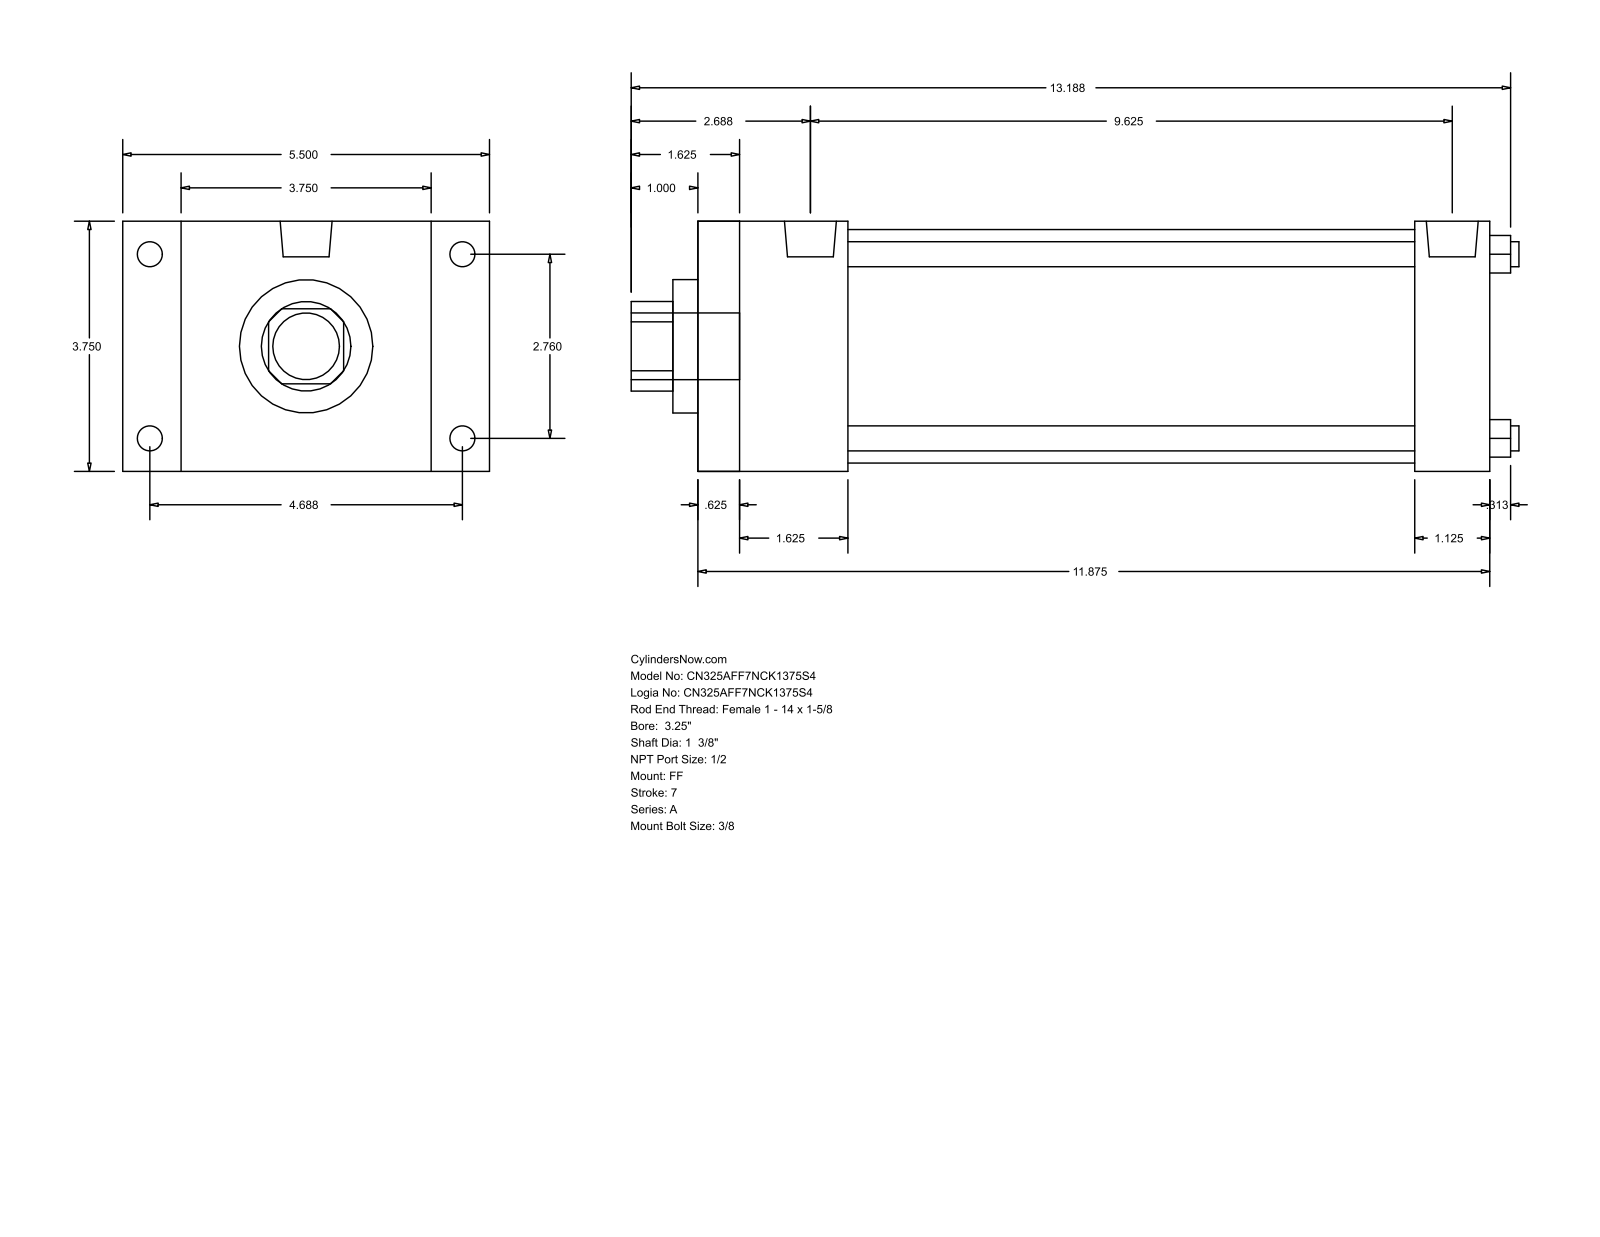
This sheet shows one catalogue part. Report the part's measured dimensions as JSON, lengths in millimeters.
{"part_name": "A_FF__0325_1.375", "step_written_by": "GSSL Pune (CONFIG_CONTROL_DESIGN)", "units": "millimeters", "bodies": {"solids": 0, "faces": 92, "planar": 64, "cylindrical": 28, "other": 0}, "overall_size": [338.14, 139.7, 95.25], "round_holes": [[9.53, 4], [34.92, 1], [50.8, 1], [88.9, 1]], "round_bosses_or_shafts": [[9.53, 4], [8.73, 4], [19.77, 2], [25.4, 1]], "partial_cylinders_radius": [[17.06, 1]], "face_to_face_distances": [95.24, 301.62, 285.75, 15.87, 22.23, 117.47, 28.57, 57.15, 273.05, 41.28], "hole_center_spacings": [49.57, 70.1, 99.14]}
